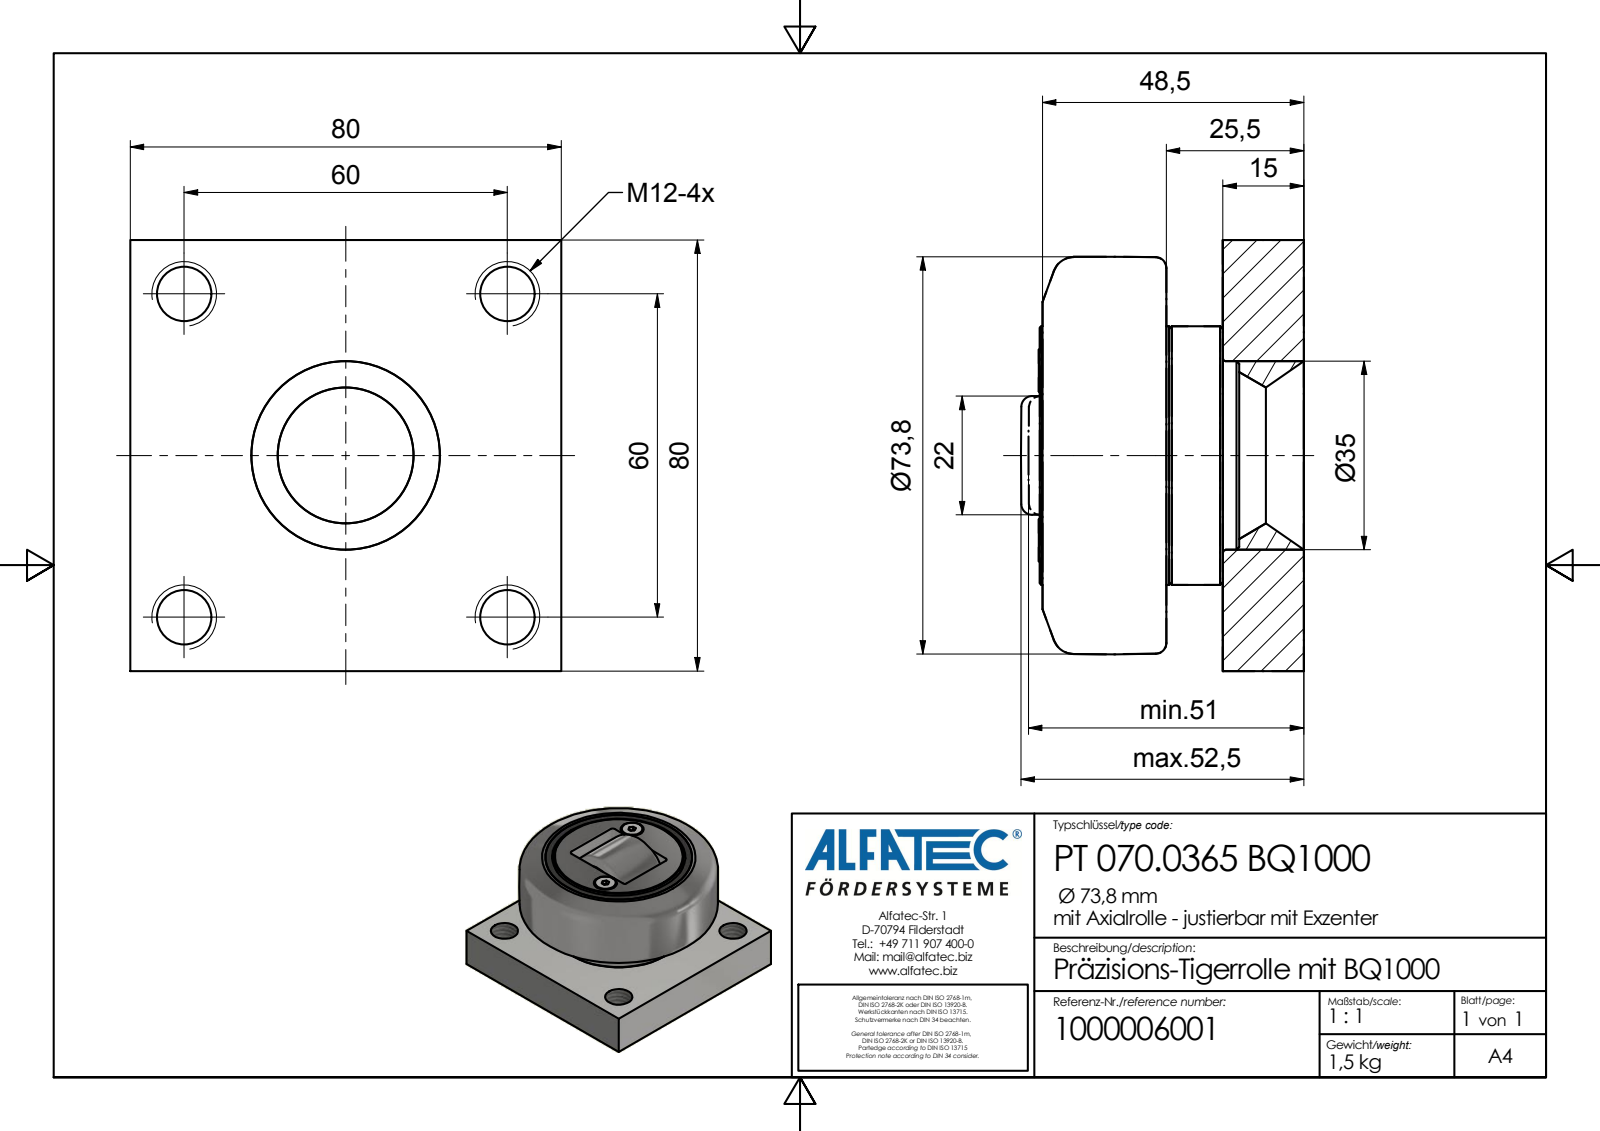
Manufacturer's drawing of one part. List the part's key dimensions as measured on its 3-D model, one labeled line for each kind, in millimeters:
Part name (STEP PRODUCT): PT 070.0365 BQ1000_Kontur
STEP written by: Autodesk Inventor 2020 (AP242_MANAGED_MODEL_BASED_3D_ENGINEERING_MIM_LF)
Units: millimetres
Bodies: 1 solid, 64 faces (36 planar, 15 cylindrical, 13 other)
Overall size (bounding box): 80 × 80 × 52.5
Volume: 201 824 mm³ · Surface area: 30 563 mm²
Round holes (diameter × count): ⌀10.11 ×4
Round bosses / shafts (diameter × count): ⌀7.8 ×2, ⌀48 ×1
Partial cylindrical surfaces — rounded edges, fillets, slot ends (radius × count): R1 ×4, R11 ×1
Main face-to-face distances: 15, 80, 25.5, 10.5, 23.5, 0.5, 49, 34, 48.5, 33.5
Hole centre spacings: 60, 84.85
